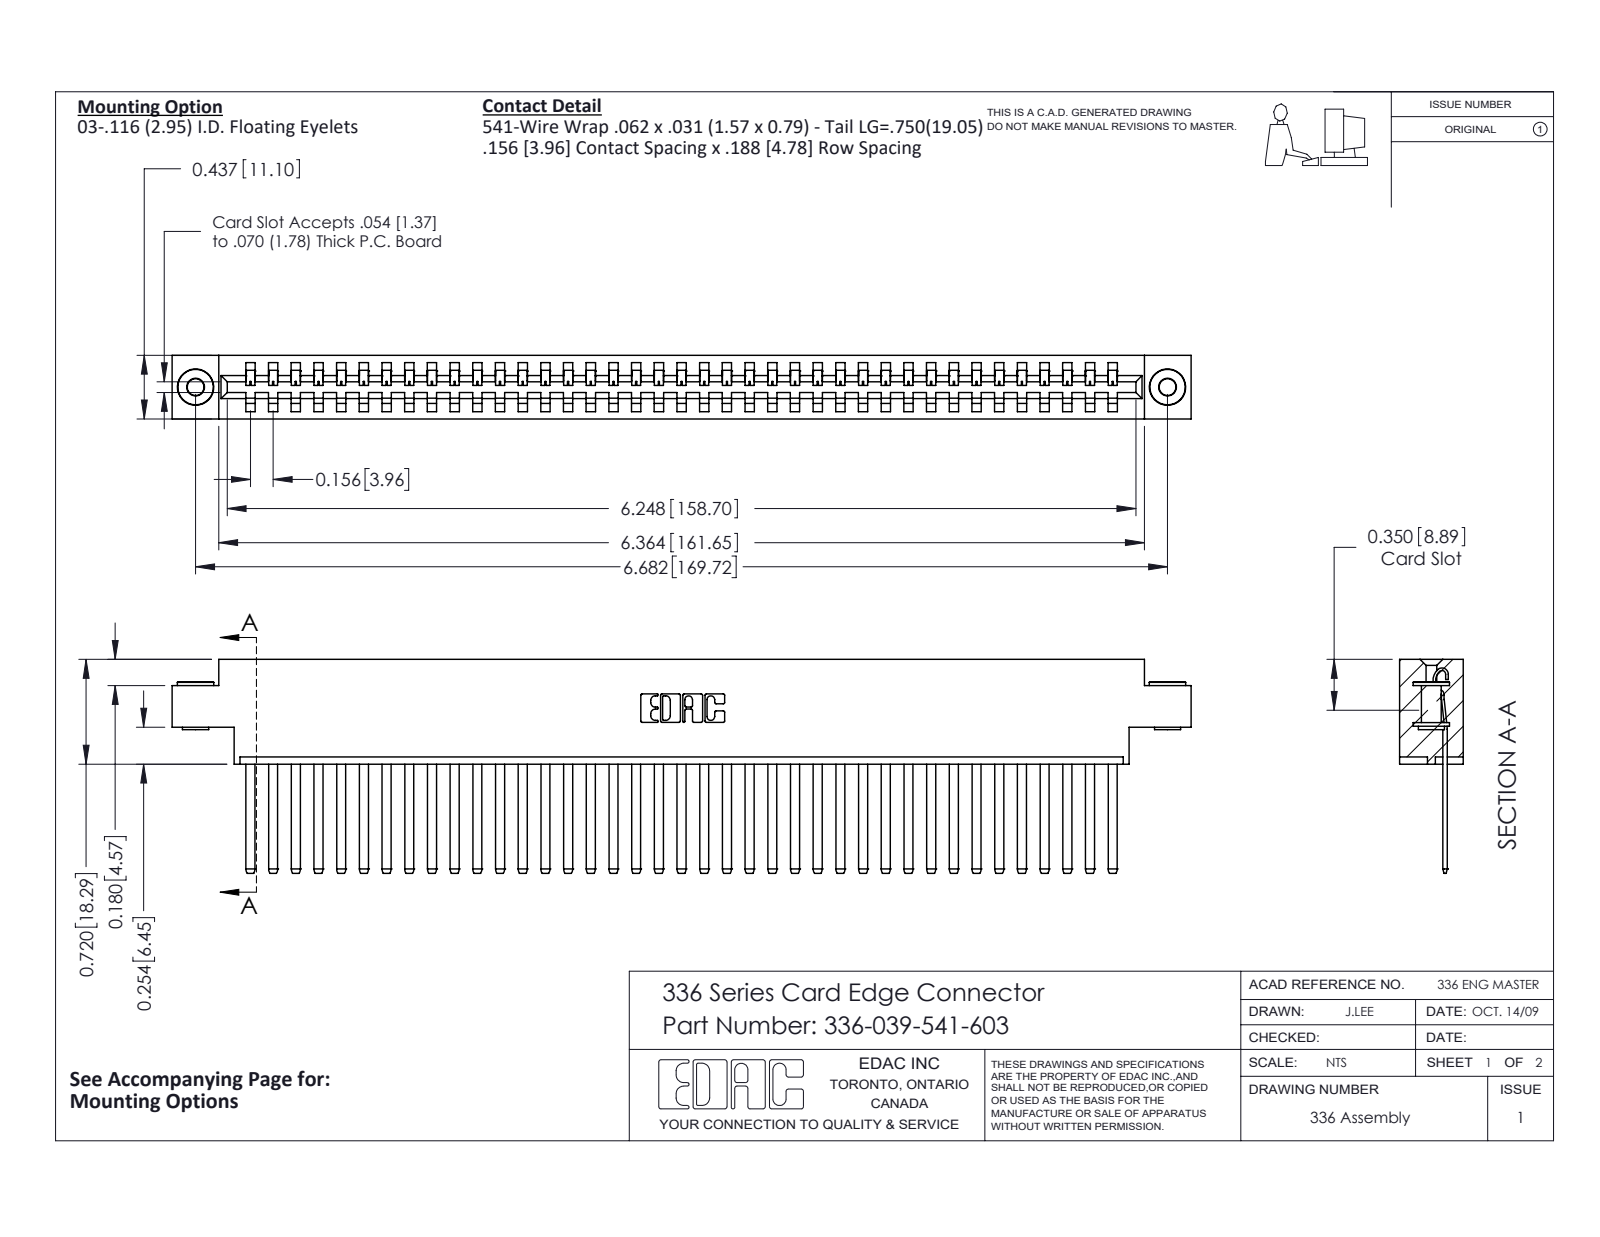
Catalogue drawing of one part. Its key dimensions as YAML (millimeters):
part_name: "345-250-002_345-250-002-102; 336-039-541-603; 336 Part_Offset - .156 Dia - TH; 336-290-001_336-290-541"
step_written_by: "SolidWorks 2020 (CONFIG_CONTROL_DESIGN)"
units: millimeters
bodies: {solids: 42, faces: 2106, planar: 1410, cylindrical: 688, other: 8}
overall_size: [177.9, 37.3, 11.1]
volume: 25860
surface_area: 28420
round_holes:
  - {diameter: 2.9, count: 2}
  - {diameter: 4, count: 2}
round_bosses_or_shafts:
  - {diameter: 6.4, count: 2}
  - {diameter: 4.6, count: 2}
  - {diameter: 3.5, count: 2}
partial_cylinders:
  - {radius: 0.1, count: 78}
  - {radius: 1.4, count: 78}
  - {radius: 0.3, count: 22}
  - {radius: 0.2, count: 6}
  - {radius: 0.8, count: 6}
  - {radius: 0.7, count: 3}
  - {radius: 0.6, count: 2}
  - {radius: 1, count: 2}
face_to_face_distances: [11.1, 0.8, 4.6, 8.3, 3.6, 7.5, 2.8, 6.5, 1.3, 9.8]
hole_center_spacings: [169.7]
